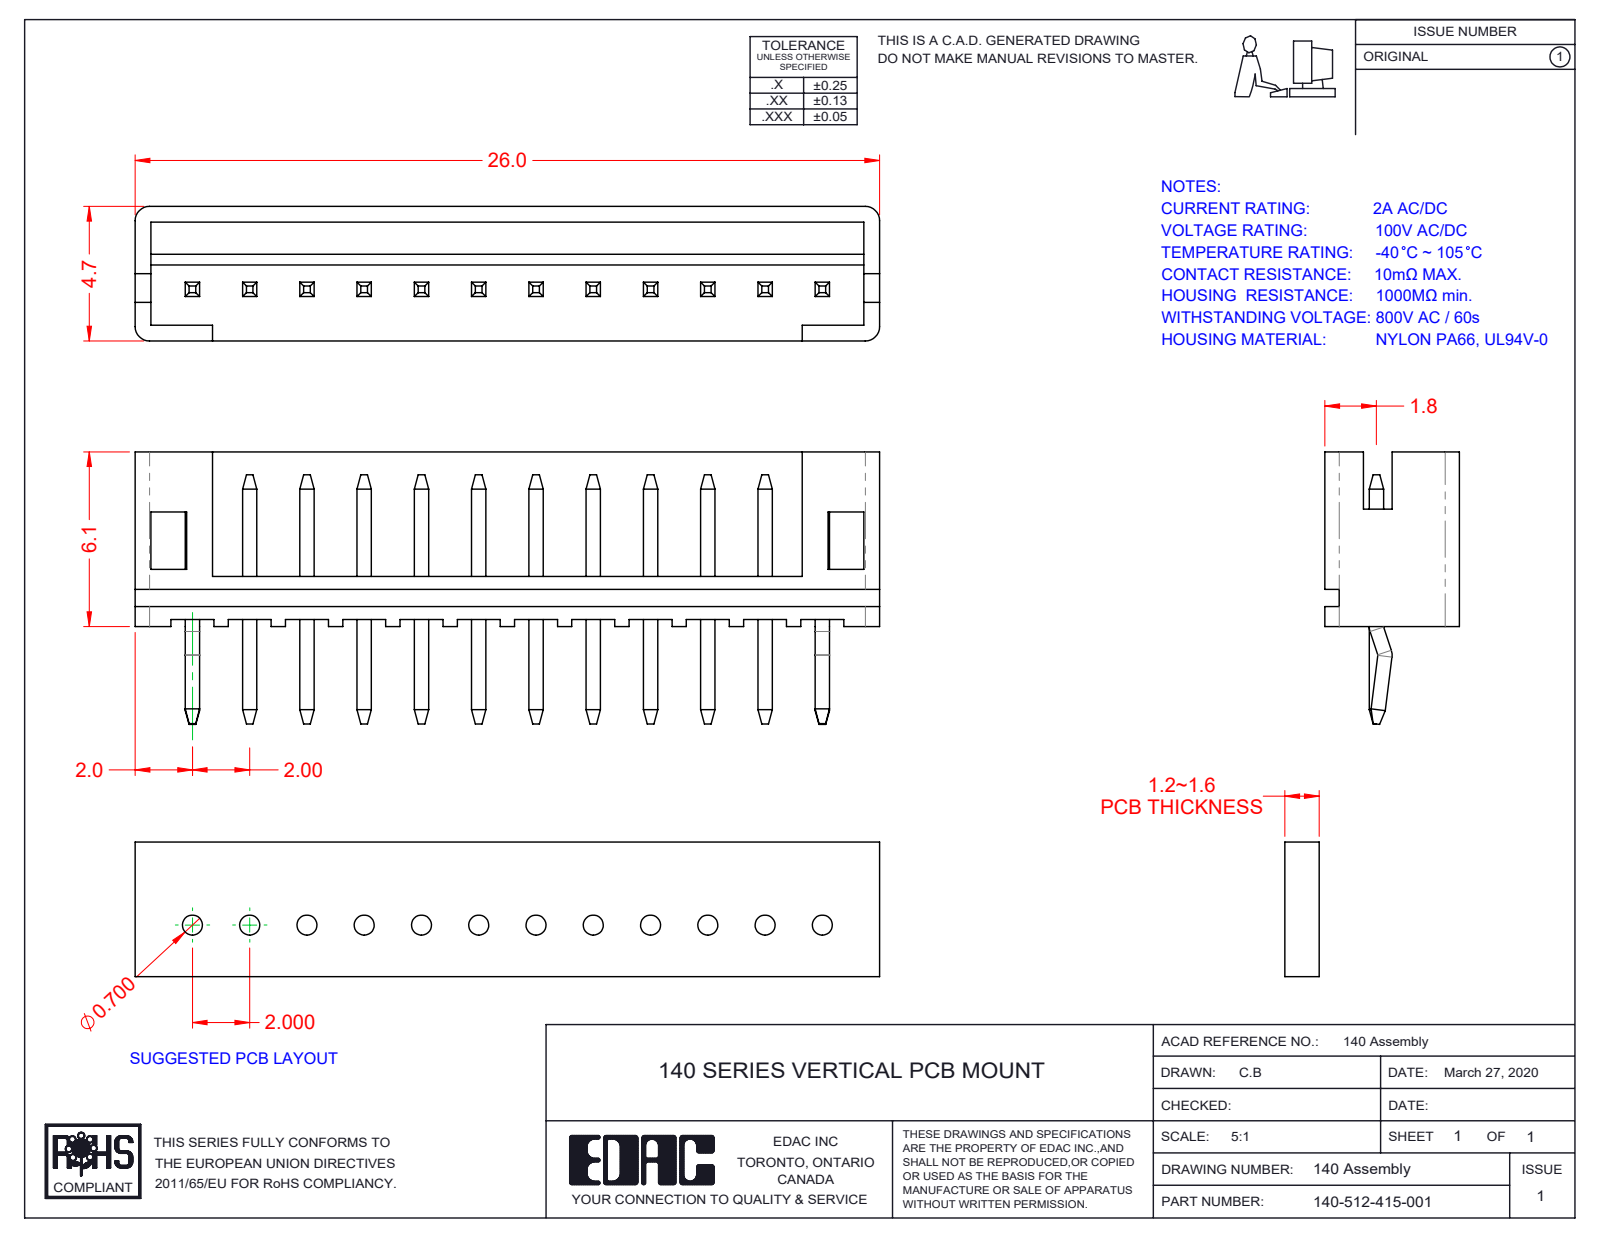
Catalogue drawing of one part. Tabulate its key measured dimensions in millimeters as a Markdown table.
| quantity | value |
| --- | --- |
| part name | V Housing_512; V Contact_Kink; V Contact_Str; 140-512-415-001 |
| STEP written by | SolidWorks 2016 (CONFIG_CONTROL_DESIGN) |
| units | millimeters |
| bodies | 13 solids, 334 faces (316 planar, 16 cylindrical, 2 other) |
| overall size | 26 × 9.52 × 4.7 |
| volume | 270 mm³ |
| surface area | 987 mm² |
| partial cylindrical surfaces (radius × count) | 0.5 × 4, 0.55 × 1 |
| main face-to-face distances | 0.55, 1.5, 0.5, 2, 2.1, 1.55, 2.65, 4.15, 1.75, 4 |
